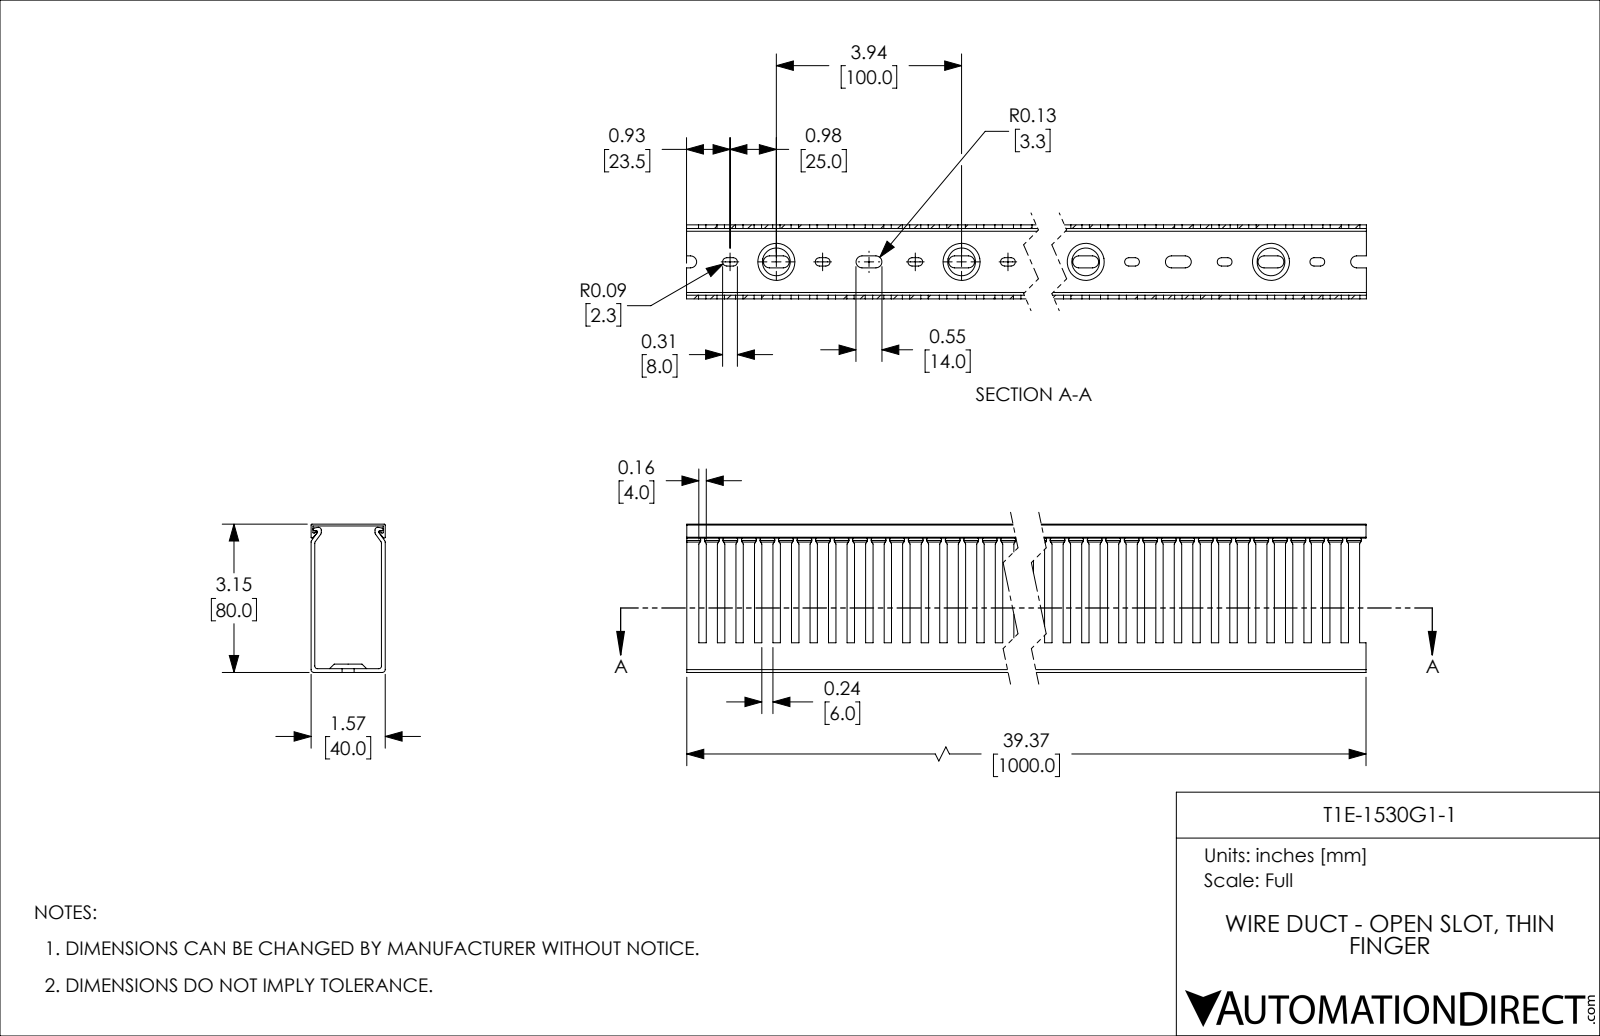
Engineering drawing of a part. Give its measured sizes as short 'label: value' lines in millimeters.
name: T1E-1530G1-1
written by: SolidWorks 2021 (CONFIG_CONTROL_DESIGN)
unit: mm
bodies: 2 solids, 775 faces (444 planar, 311 cylindrical, 20 other)
size: 1000 × 80 × 40
volume: 444 689 mm³; area: 506 715 mm²
rounds: 40× R2.25, 40× R3.25, 12× R1.5, 8× R0.5, 6× R0.75
face distances: 2, 38, 40, 36, 1, 80, 79, 77, 78, 39
